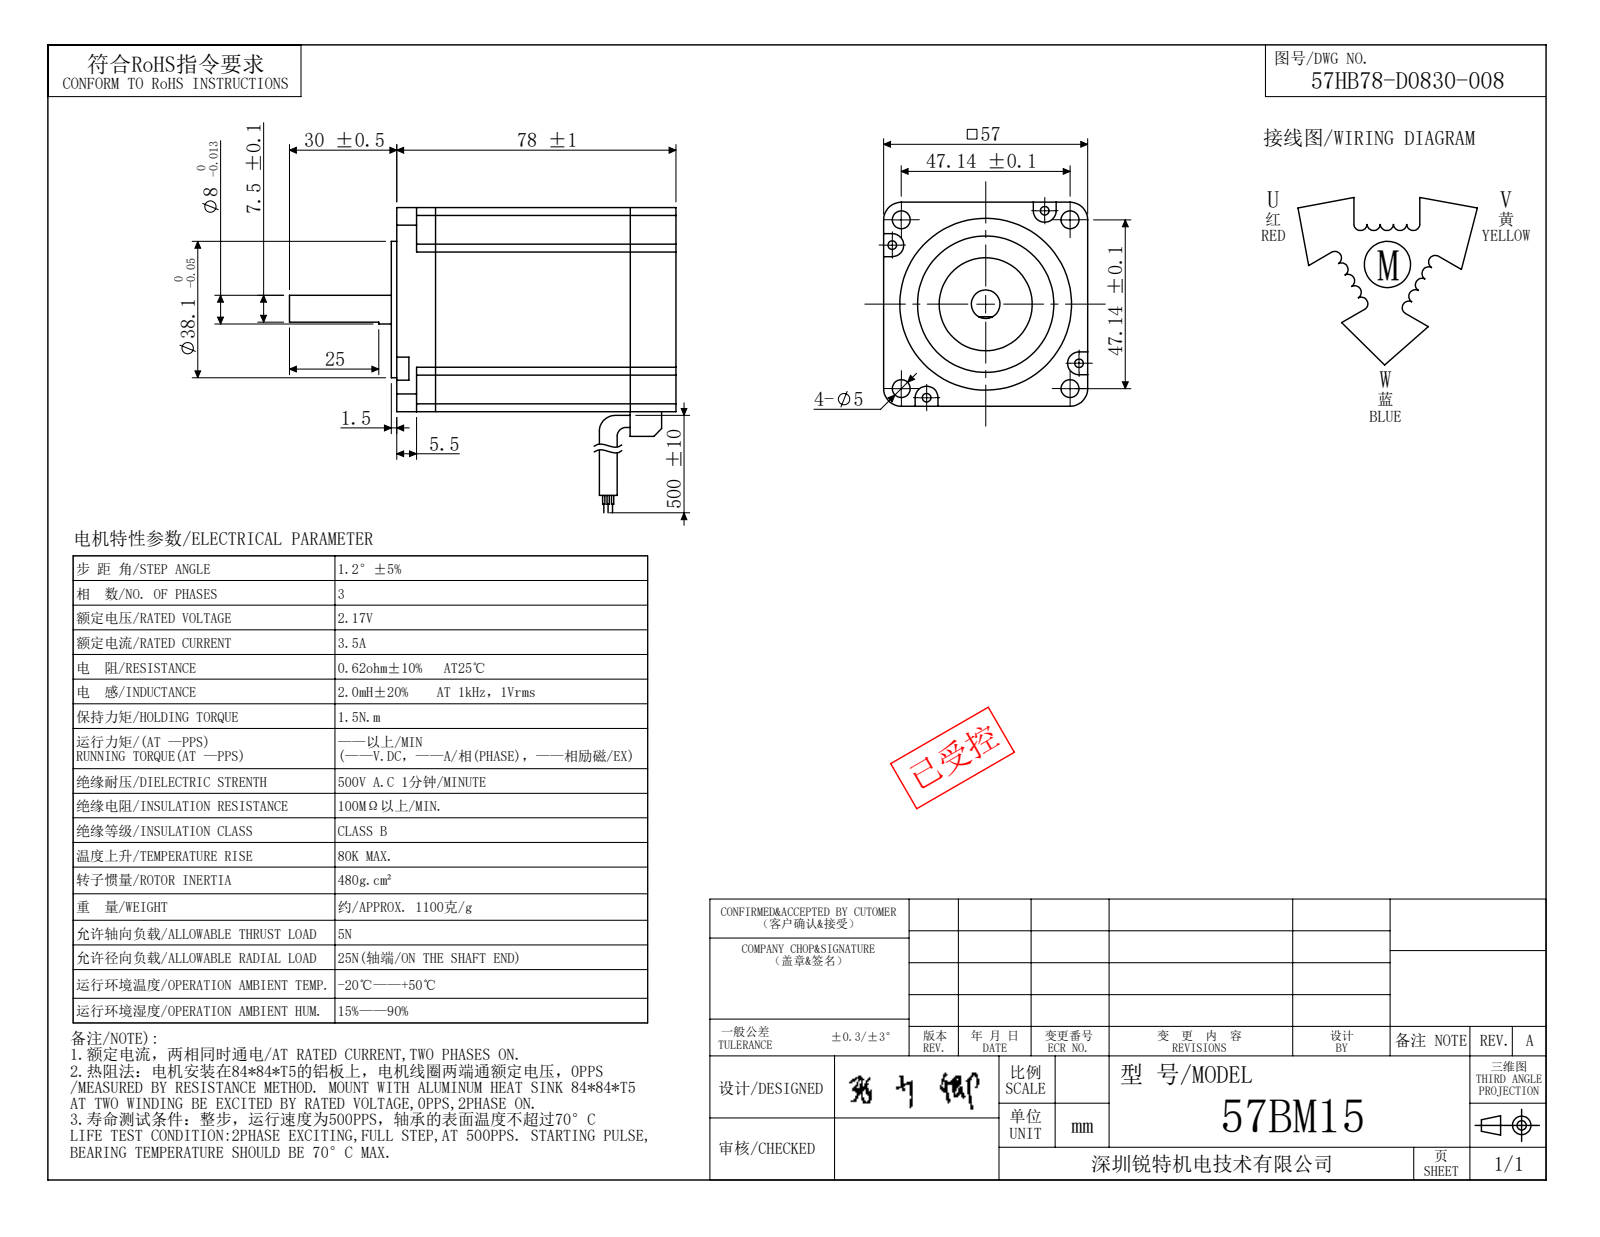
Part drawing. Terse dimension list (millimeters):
written by: SolidWorks 2020 (AUTOMOTIVE_DESIGN)
unit: mm
bodies: 1 solid, 73 faces (28 planar, 45 cylindrical, 0 other)
size: 108 × 57 × 57
volume: 226 338 mm³; area: 26 390 mm²
holes: 4× ⌀2.4, 4× ⌀5, 1× ⌀26, 1× ⌀48
bosses: 1× ⌀38.1, 1× ⌀8
rounds: 8× R2.2, 4× R3.2, 4× R4.93, 4× R8
face distances: 57, 78, 77.25, 0.75, 79.5, 2.25, 1.5, 78.3, 1.05, 1.2
hole spacings: 7.51, 30.88, 33.33, 40.15, 43.67, 47.14, 50.17, 63.82
